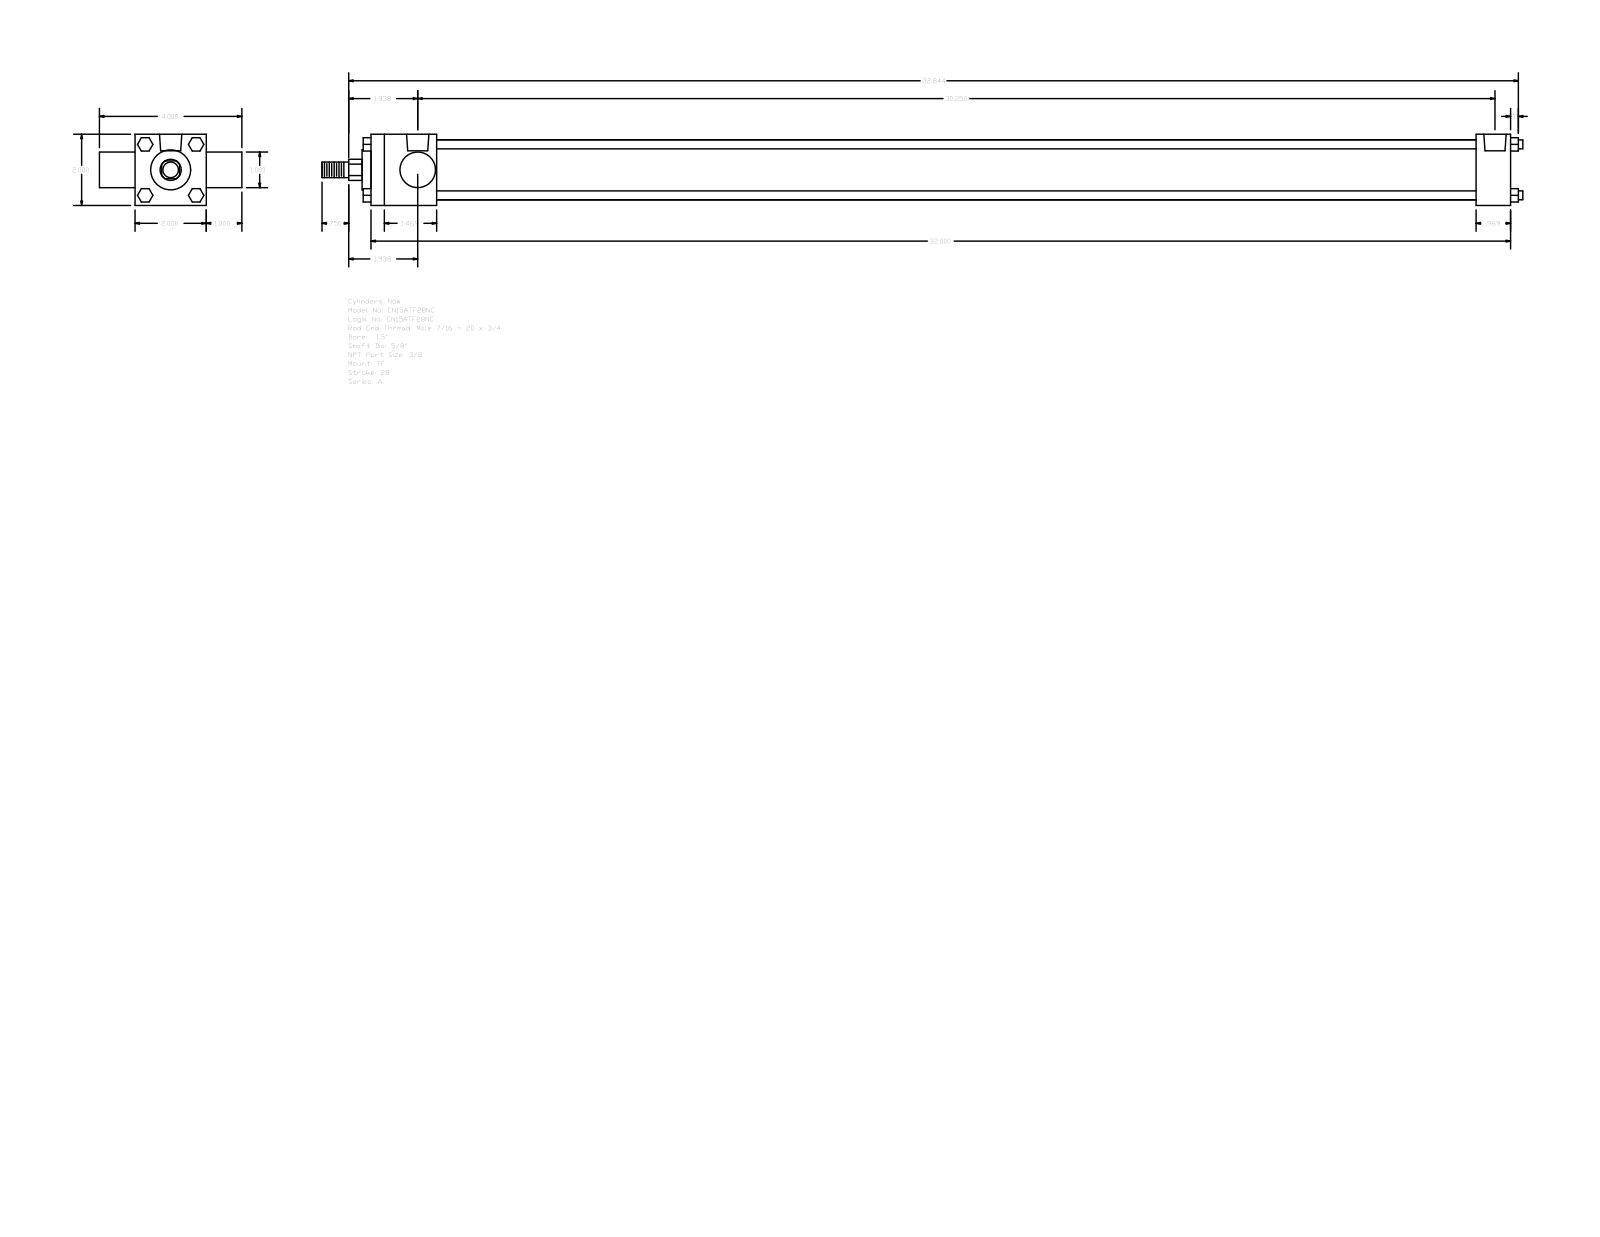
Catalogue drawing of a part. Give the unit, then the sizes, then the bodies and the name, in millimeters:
Units: millimetres
Overall size (bounding box): 856.46 × 101.6 × 50.8
Round holes (diameter × count): ⌀5.56 ×3, ⌀15.93 ×2
Round bosses / shafts (diameter × count): ⌀6.35 ×4, ⌀42.93 ×1, ⌀28.57 ×1, ⌀25.4 ×1, ⌀15.88 ×1, ⌀11.11 ×1
Partial cylindrical surfaces — rounded edges, fillets, slot ends (radius × count): R7.54 ×1
Main face-to-face distances: 50.8, 812.79, 25.4, 76.2, 46.83, 788.19, 741.36, 765.96, 24.6, 101.6
Hole centre spacings: 3.97, 764.38, 760.41, 768.35
Bodies: 0 solids, 120 faces (92 planar, 28 cylindrical, 0 other)
Part name (STEP PRODUCT): A_TF__0150_0.625
STEP written by: GSSL Pune (CONFIG_CONTROL_DESIGN)
